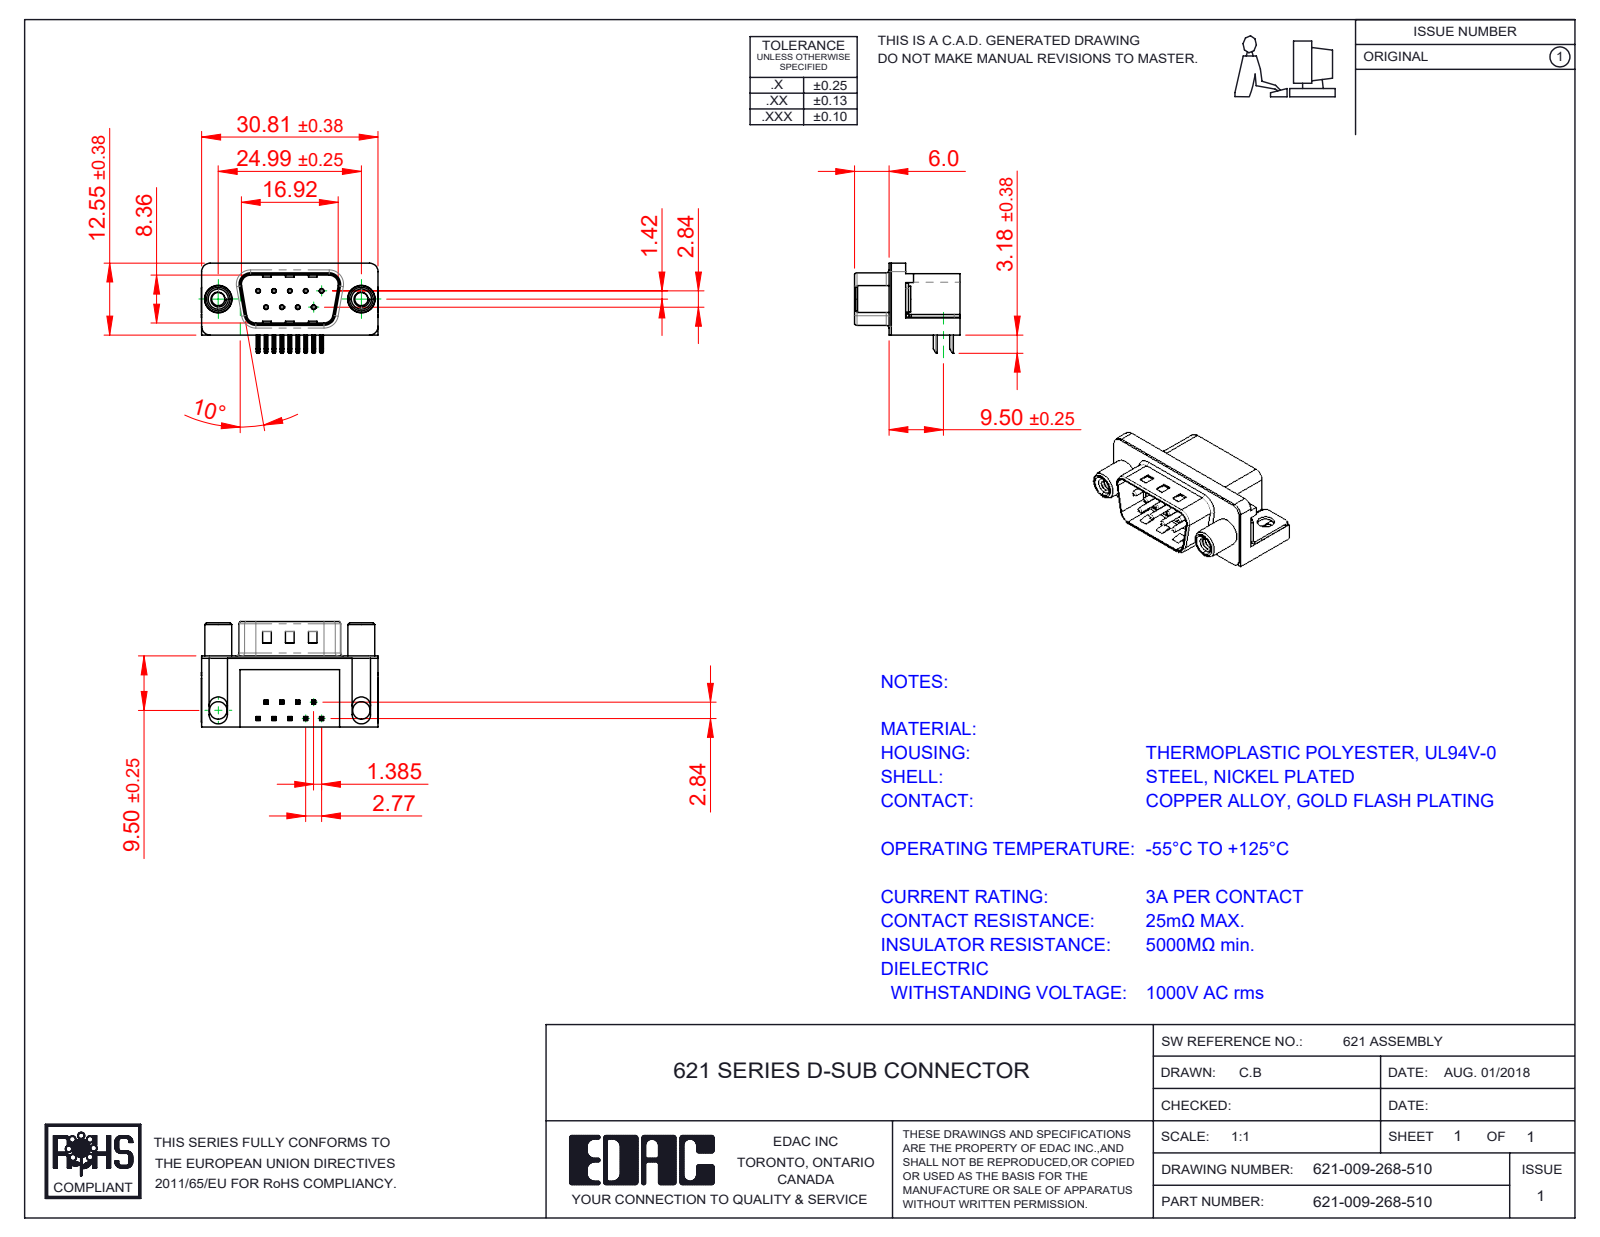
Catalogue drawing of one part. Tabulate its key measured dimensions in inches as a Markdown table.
| quantity | value |
| --- | --- |
| part name | 621 Round Threaded Standoff; 621 Contact Top; 621-009-268-510; 621 Shell_9 Socket (+3 more) |
| STEP written by | SolidWorks 2016 (CONFIG_CONTROL_DESIGN) |
| units | inches |
| bodies | 15 solids, 983 faces (563 planar, 323 cylindrical, 97 other) |
| overall size | 1.216 × 0.724 × 0.619 |
| volume | 0.203 in³ |
| surface area | 7.141 in² |
| round holes (diameter × count) | 0.014 × 9, 0.031 × 9, 0.091 × 2, 0.12 × 2, 0.122 × 2, 0.157 × 2, 0.189 × 2, 0.197 × 2 |
| round bosses / shafts (diameter × count) | 0.03 × 9, 0.193 × 2, 0.185 × 2, 0.177 × 2, 0.152 × 2 |
| partial cylindrical surfaces (radius × count) | 0.01 × 36, 0.005 × 18, 0.039 × 16, 0.02 × 9, 0.059 × 8, 0.063 × 8, 0.035 × 4, 0.079 × 4 |
| main face-to-face distances | 0.016, 0.472, 0.488, 0.407, 0.114, 0.374, 0.098, 0.02, 0.083, 0.014 |
| hole center spacings | 0.124, 0.109, 0.218, 0.198, 0.198, 0.327, 0.294, 0.295 |
